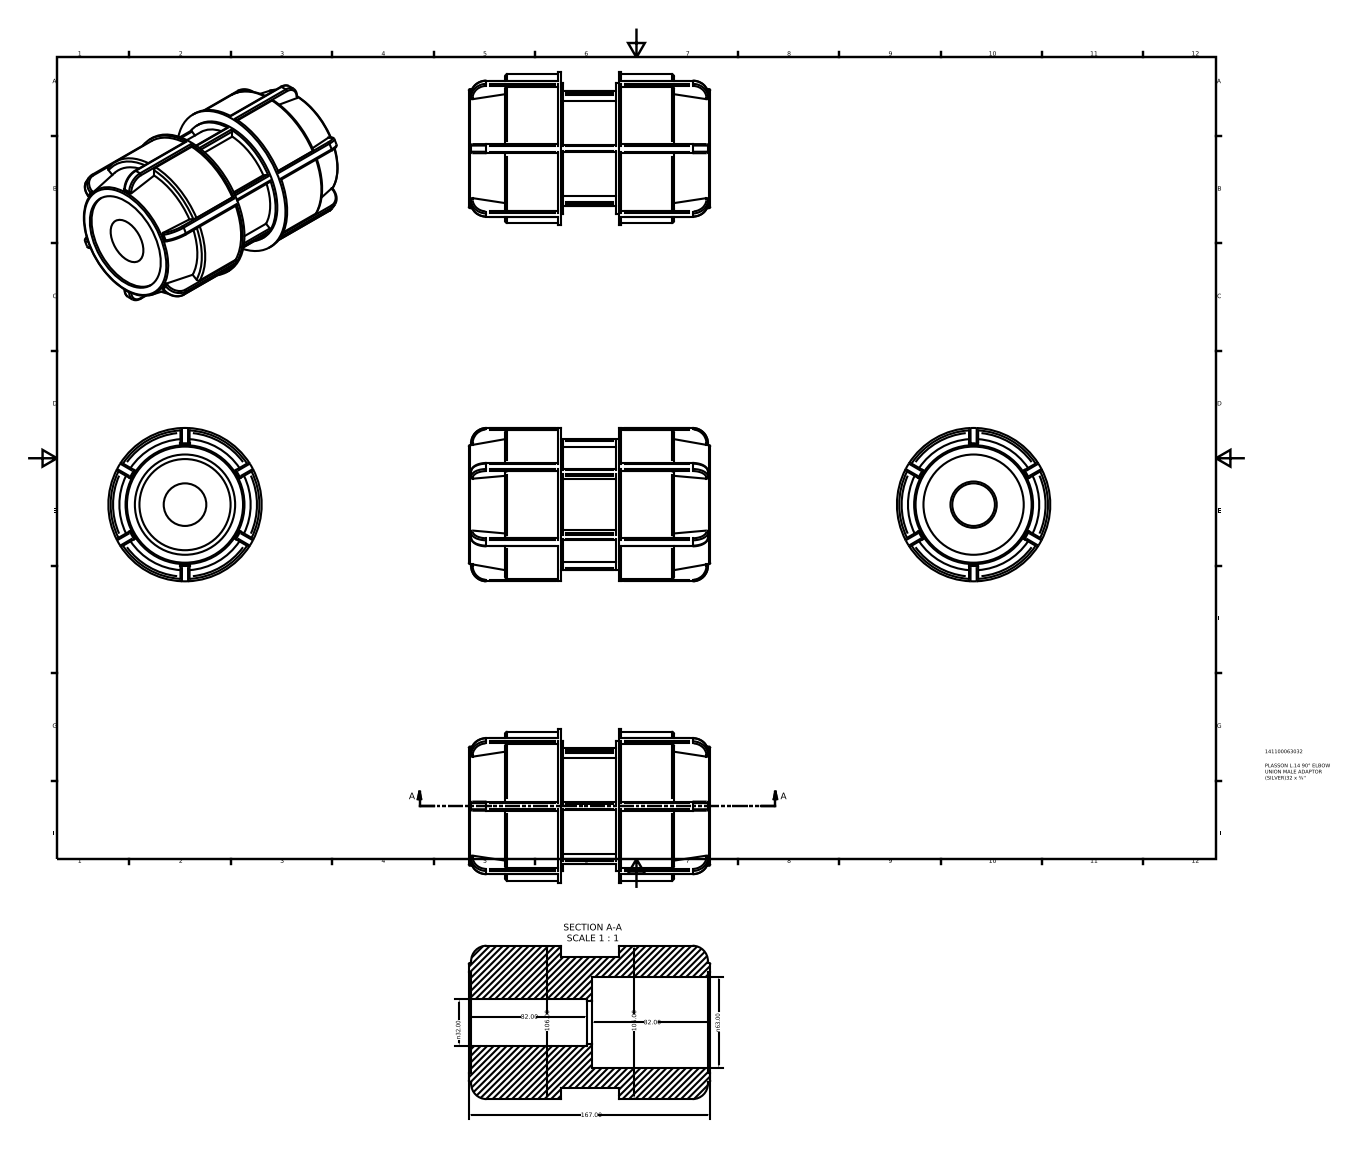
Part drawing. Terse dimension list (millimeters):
name: 141100063032
written by: Autodesk Inventor 2015 (AUTOMOTIVE_DESIGN)
unit: mm
bodies: 1 solid, 230 faces (92 planar, 86 cylindrical, 52 other)
size: 167 × 106 × 106
volume: 832 114 mm³; area: 102 205 mm²
holes: 1× ⌀29.44, 1× ⌀32, 1× ⌀63, 1× ⌀69.3
bosses: 1× ⌀106, 1× ⌀102.82, 1× ⌀90.1, 1× ⌀79.5
rounds: 44× R1.06
face distances: 40.08, 101.87, 1.67, 38.41, 63.46, 61.79, 103.54, 83.33, 18.54, 21.54
